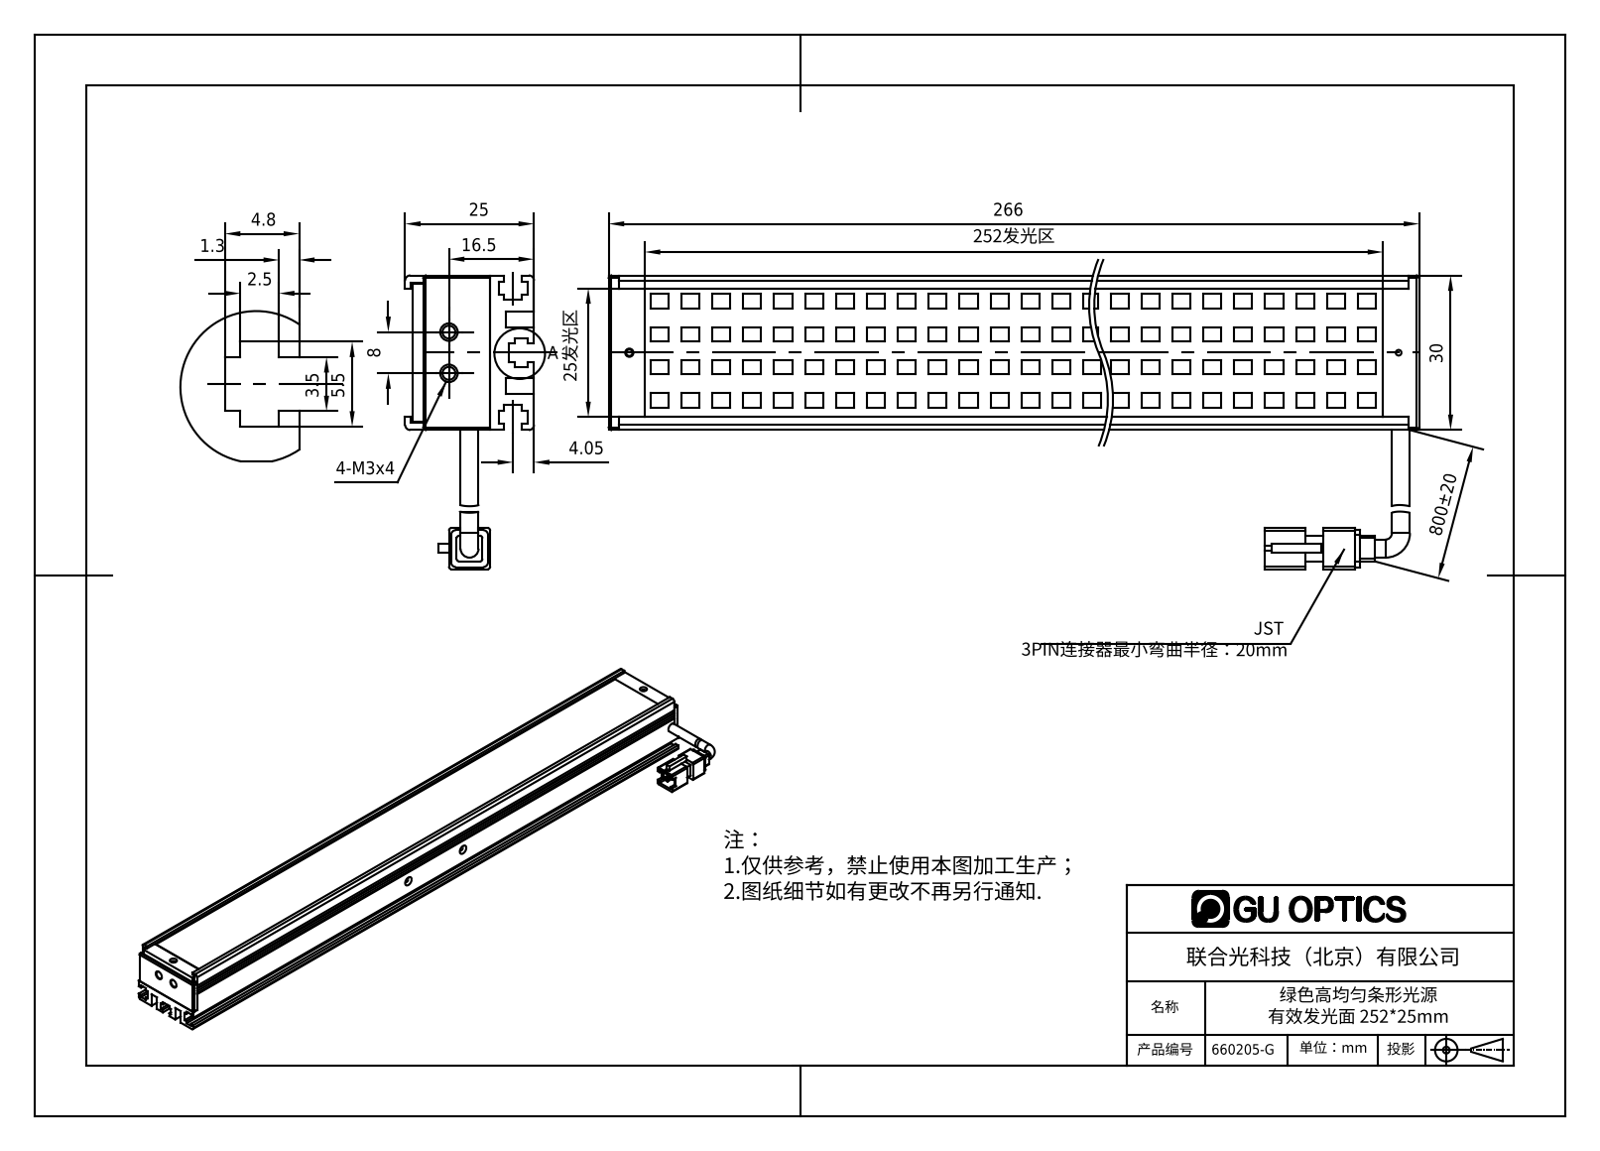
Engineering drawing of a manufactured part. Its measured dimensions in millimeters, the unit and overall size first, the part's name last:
Units: millimetres
Overall size (bounding box): 266 × 57 × 25
Round holes (diameter × count): ⌀1.6 ×5, ⌀1.5 ×2, ⌀1.7 ×2, ⌀2.5 ×2, ⌀2.8 ×2, ⌀3 ×2, ⌀1.1 ×1, ⌀1.25 ×1, ⌀2 ×1
Round bosses / shafts (diameter × count): ⌀3.5 ×2
Partial cylindrical surfaces — rounded edges, fillets, slot ends (radius × count): R1 ×12, R0.5 ×8, R1.65 ×1
Main face-to-face distances: 1, 13, 2, 2.5, 3, 27.5, 9.5, 4.5, 12, 15.1
Hole centre spacings: 258, 7, 114, 114.19, 144, 144.15, 258.09, 8
Volume: 90 767 mm³ · Surface area: 92 489 mm²
Bodies: 6 solids, 1284 faces (1098 planar, 83 cylindrical, 103 other)
Part name (STEP PRODUCT): 660205-G
STEP written by: SolidWorks 2016 (AUTOMOTIVE_DESIGN)
